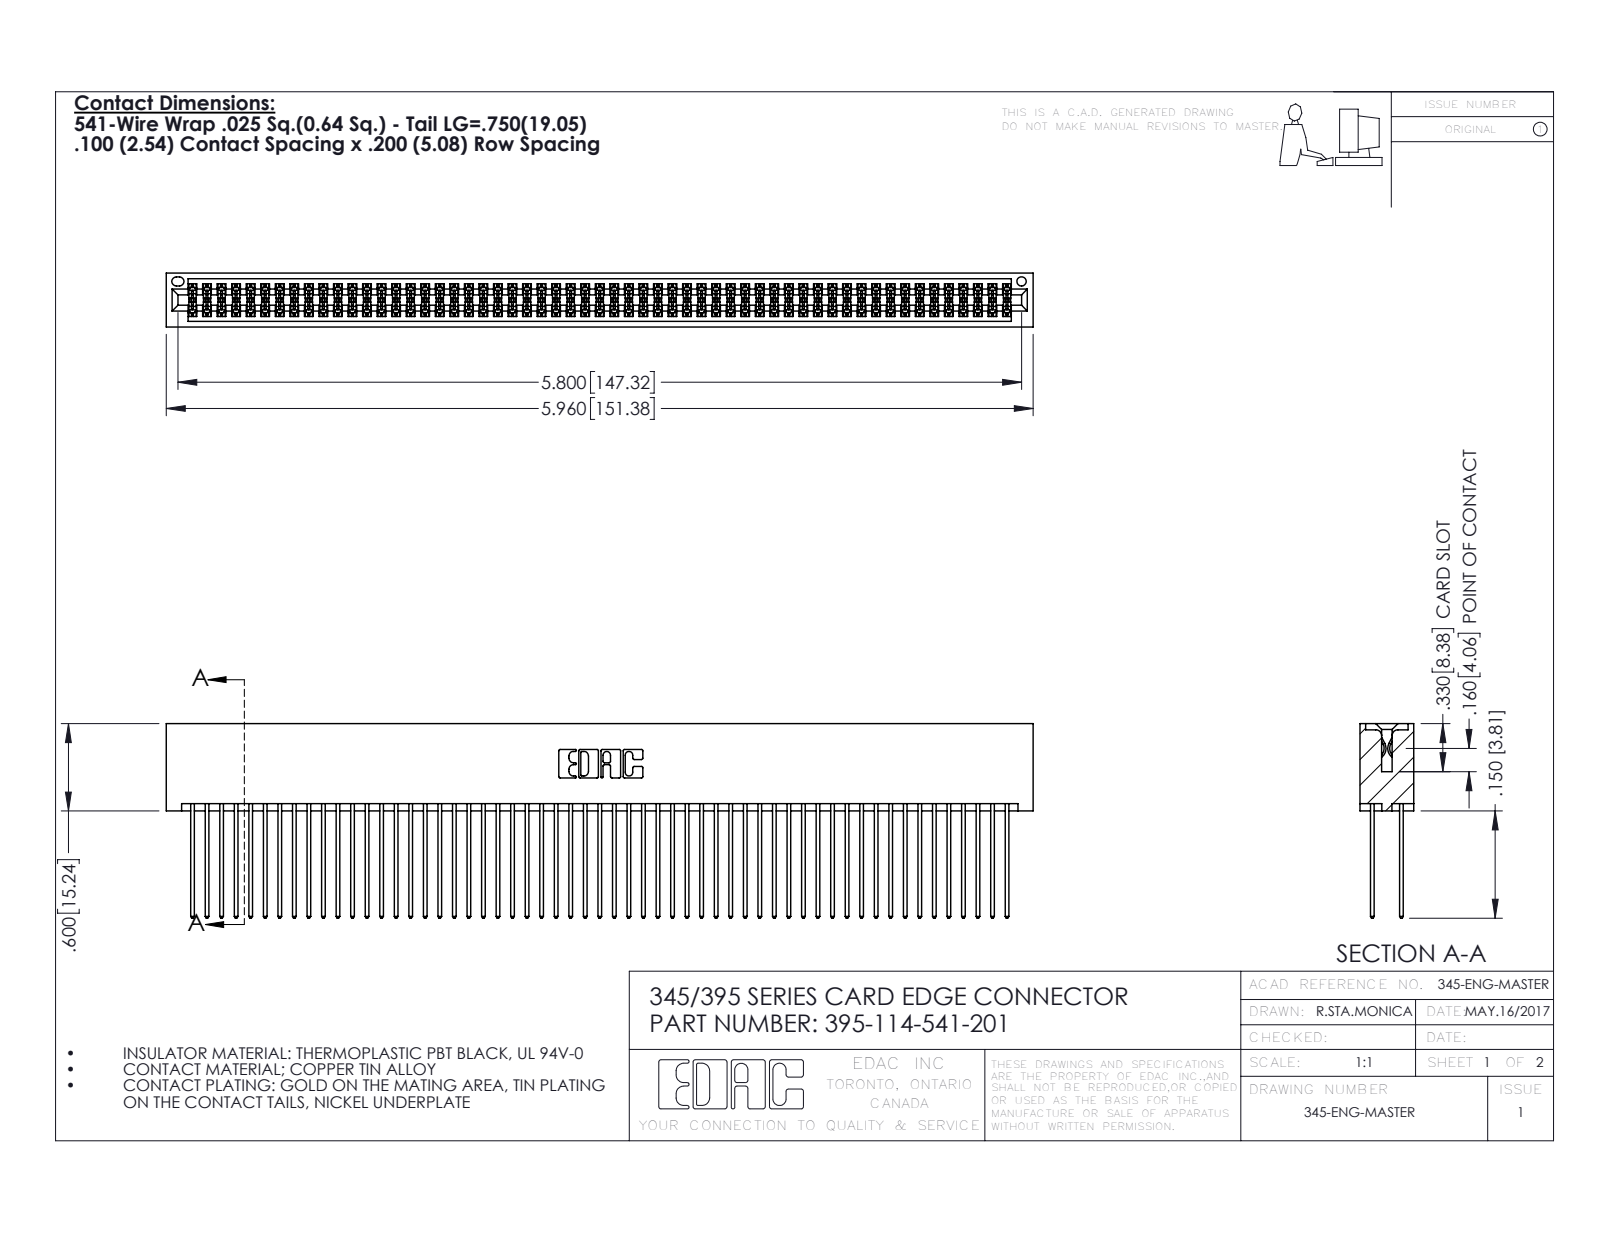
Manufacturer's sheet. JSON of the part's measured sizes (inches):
{"part_name": "345-292-001_345-293-141; 345 Part_No Mounting Lugs; 395-114-541-201", "step_written_by": "SolidWorks 2016 (CONFIG_CONTROL_DESIGN)", "units": "inches", "bodies": {"solids": 115, "faces": 5818, "planar": 3838, "cylindrical": 1980, "other": 0}, "overall_size": [5.96, 1.337, 0.37], "volume_in3": 0.983, "surface_area_in2": 42.61, "round_holes": [[0.064, 1]], "partial_cylinders_radius": [[0.006, 171], [0.01, 114], [0.01, 22], [0.007, 6], [0.031, 6], [0.026, 3], [0.014, 2], [0.019, 2]], "face_to_face_distances": [0.298, 0.072, 0.2, 0.098, 0.272, 0.025, 0.225, 0.37, 0.175, 0.149]}
